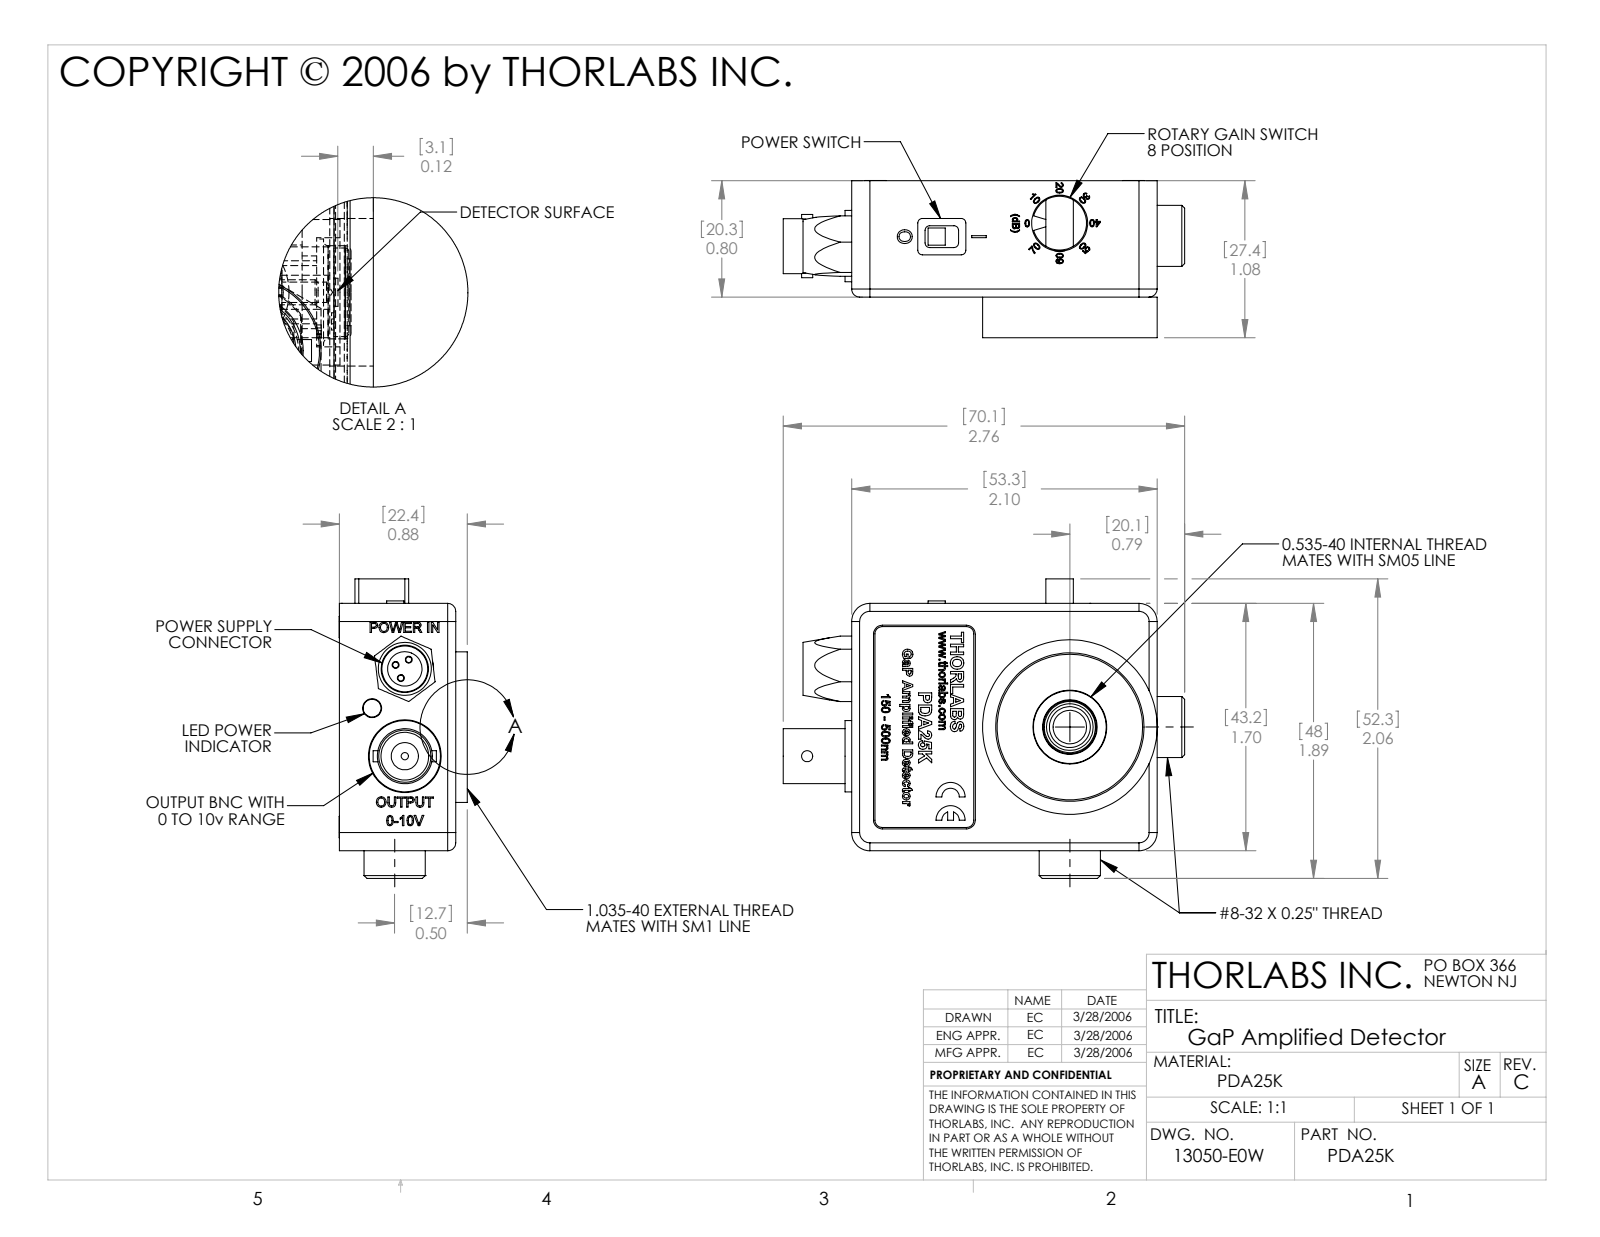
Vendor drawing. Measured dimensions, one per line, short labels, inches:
name: 13050-E0W
written by: SolidWorks 2011 (CONFIG_CONTROL_DESIGN)
unit: in
bodies: 0 solids, 525 faces (337 planar, 87 cylindrical, 101 other)
size: 2.761 × 2.058 × 1.082
holes: 3× ⌀0.039, 2× ⌀0.136, 1× ⌀0.05, 1× ⌀0.13, 1× ⌀0.23, 1× ⌀0.315, 1× ⌀0.325, 1× ⌀0.328, 1× ⌀0.375, 1× ⌀0.385, 1× ⌀0.507, 1× ⌀1
bosses: 4× ⌀0.147, 2× ⌀0.42, 1× ⌀1.2, 1× ⌀0.49, 1× ⌀0.378, 1× ⌀0.37, 1× ⌀0.32, 1× ⌀0.236
rounds: 8× R0.031, 8× R0.095, 4× R0.055, 4× R0.125, 3× R0.062, 2× R0.05, 1× R0.063
face distances: 0.063, 0.502, 0.439, 0.298, 0.8, 0.737, 1.7, 0.02, 0.78, 0.717
hole spacings: 0.069, 0.098, 0.112, 0.138, 0.202, 0.212, 0.286, 0.339
